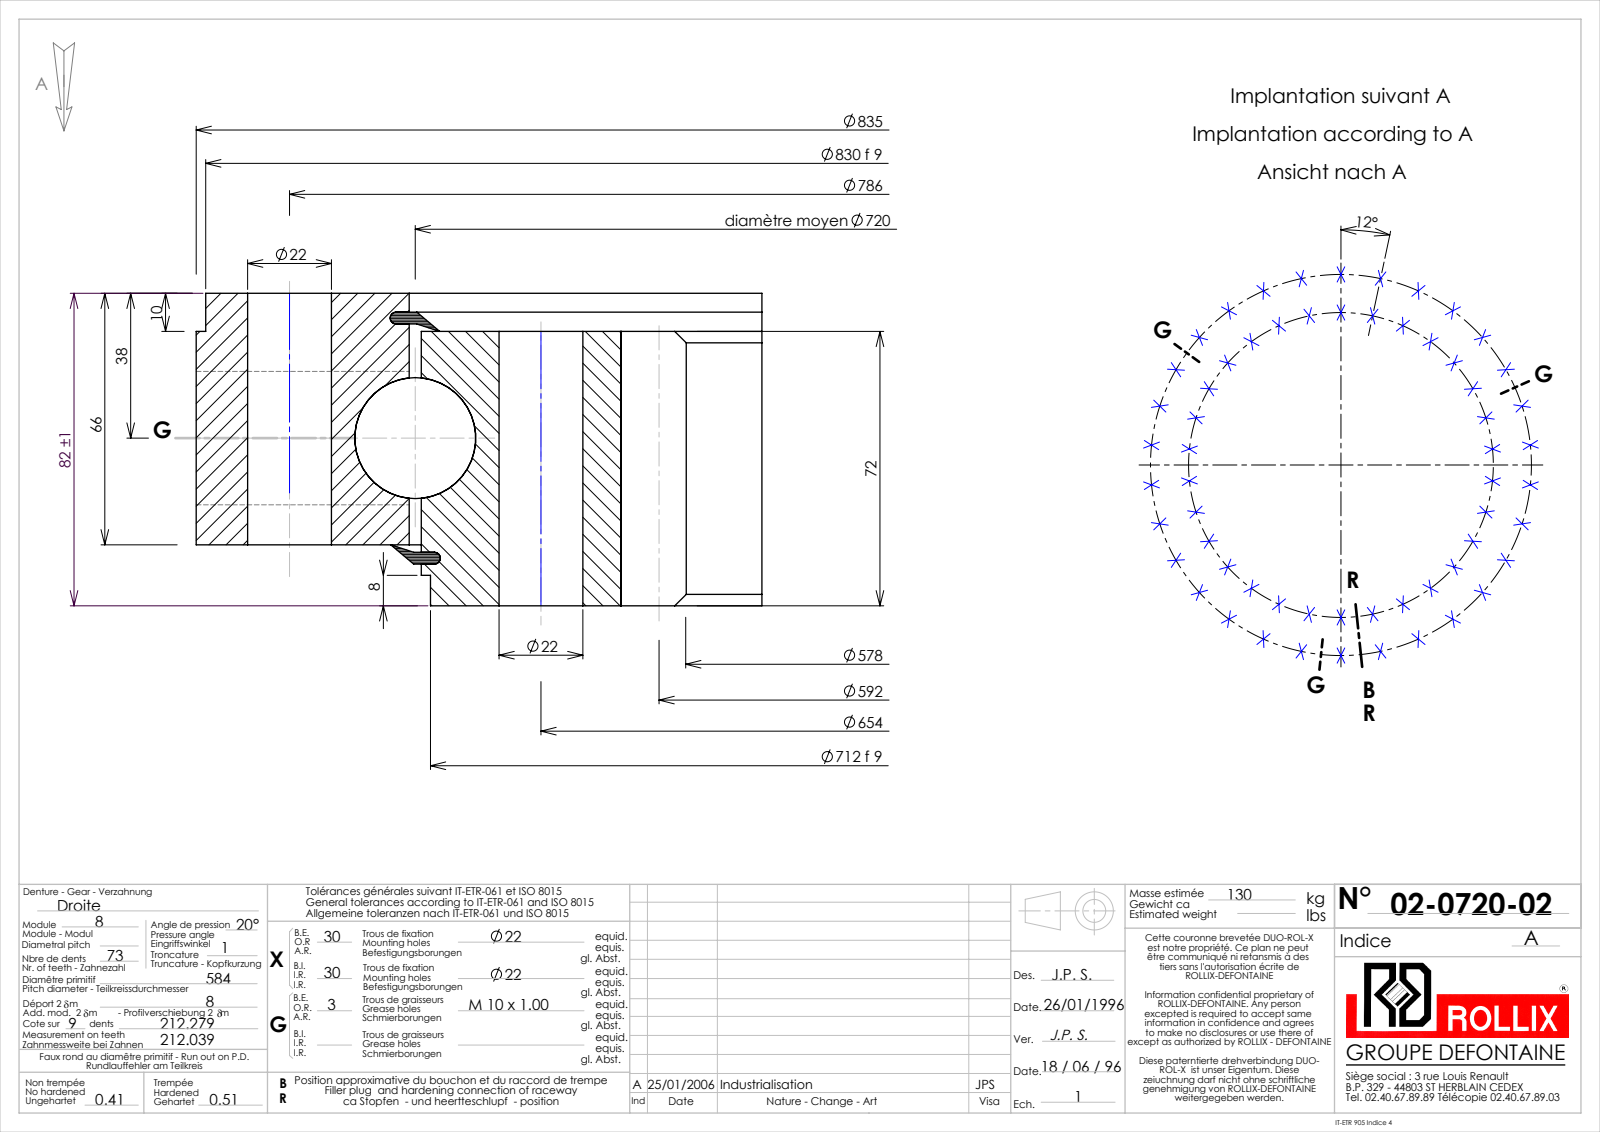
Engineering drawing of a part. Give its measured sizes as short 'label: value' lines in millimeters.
name: 02-0720-02
written by: SolidWorks 2016 (CONFIG_CONTROL_DESIGN)
unit: mm
bodies: 5 solids, 626 faces (160 planar, 291 cylindrical, 175 other)
size: 835 × 835 × 82
volume: 14 980 000 mm³; area: 1 756 000 mm²
holes: 60× ⌀22, 3× ⌀9, 1× ⌀723.17
bosses: 1× ⌀835, 1× ⌀830, 1× ⌀716.83, 1× ⌀712
rounds: 1× R289, 1× R306
face distances: 56, 66, 10, 16, 72, 82, 5.05, 61.05, 3.1, 1.95
hole spacings: 486.02, 597.46, 202.1, 327, 266.01, 384.41, 639.71, 68.36
